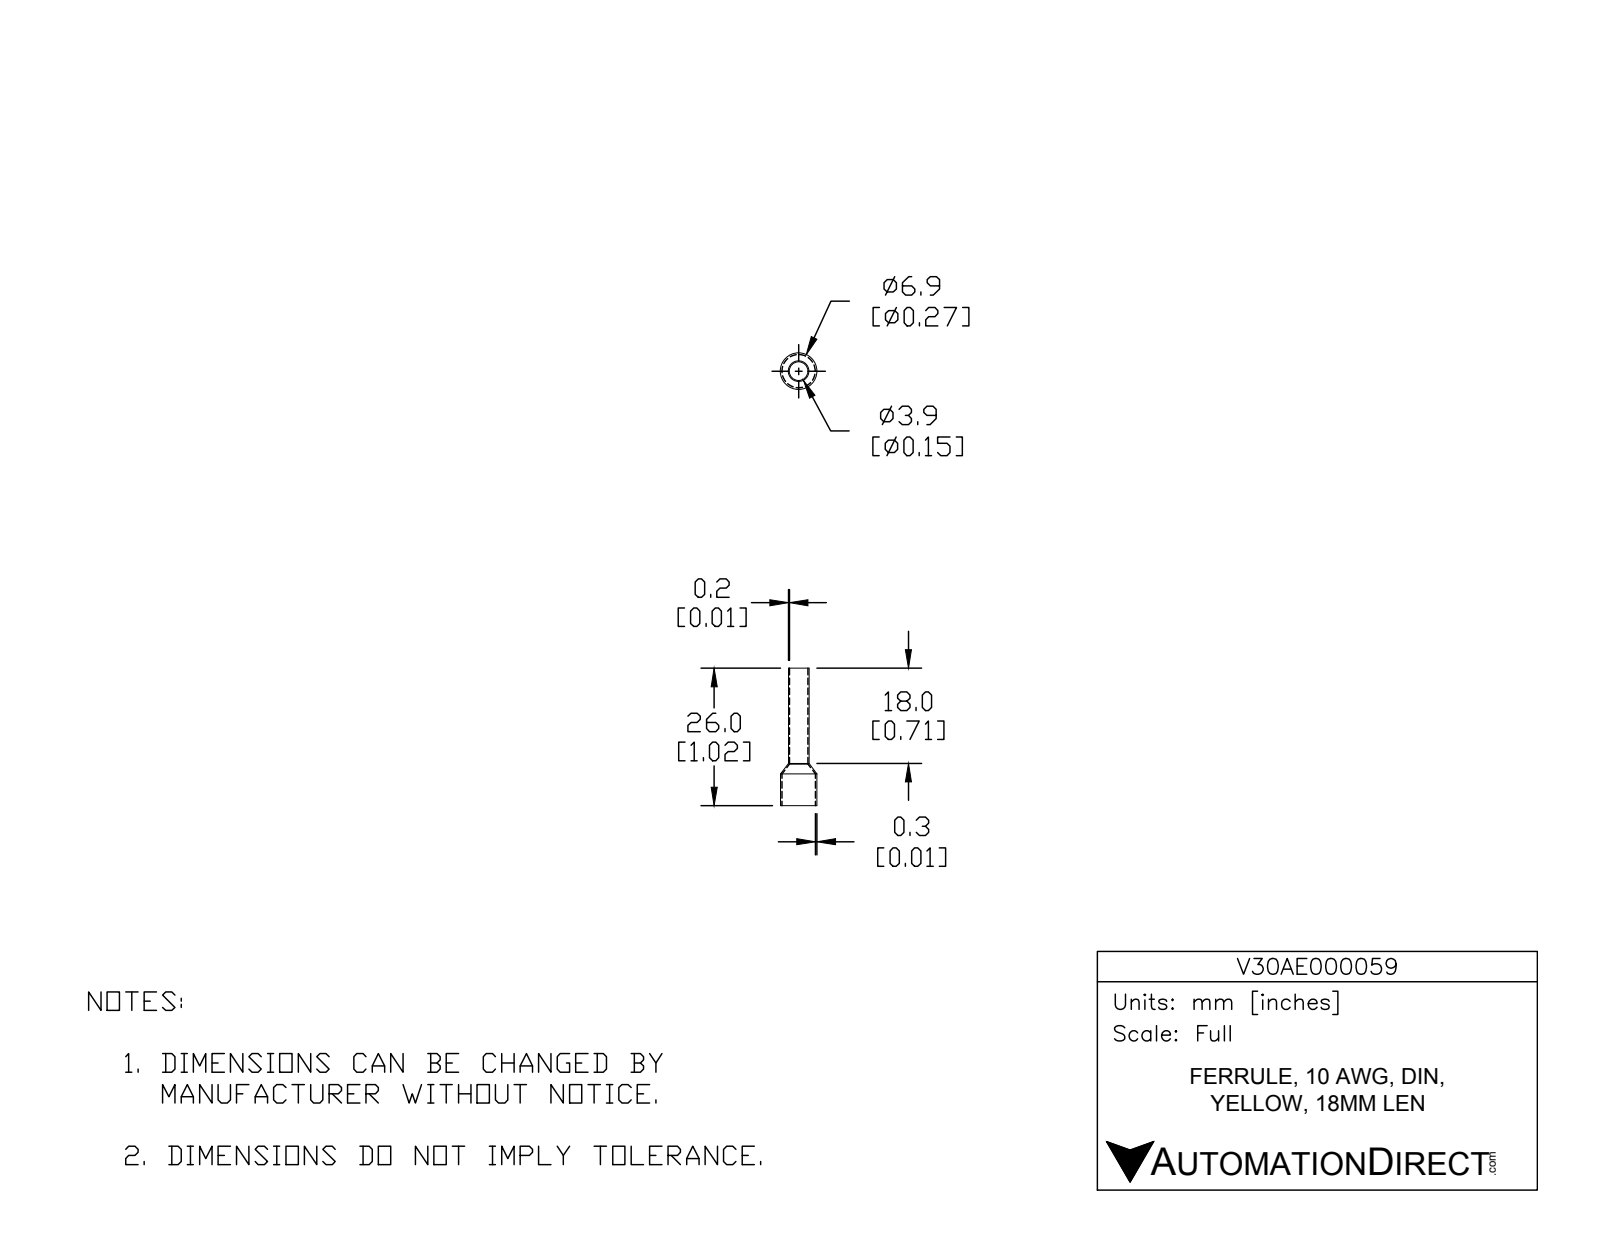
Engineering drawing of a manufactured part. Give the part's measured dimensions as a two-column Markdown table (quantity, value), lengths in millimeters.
| quantity | value |
| --- | --- |
| part name | V30AE000059 |
| STEP written by | SolidWorks 2017 (AUTOMOTIVE_DESIGN) |
| units | millimeters |
| bodies | 1 solid, 14 faces (2 planar, 8 cylindrical, 4 other) |
| overall size | 26 × 6.9 × 6.9 |
| volume | 89 mm³ |
| surface area | 756 mm² |
| round holes (diameter × count) | 3.5 × 1, 6.3 × 1 |
| round bosses / shafts (diameter × count) | 6.9 × 1, 3.9 × 1 |
| main face-to-face distances | 26 |
